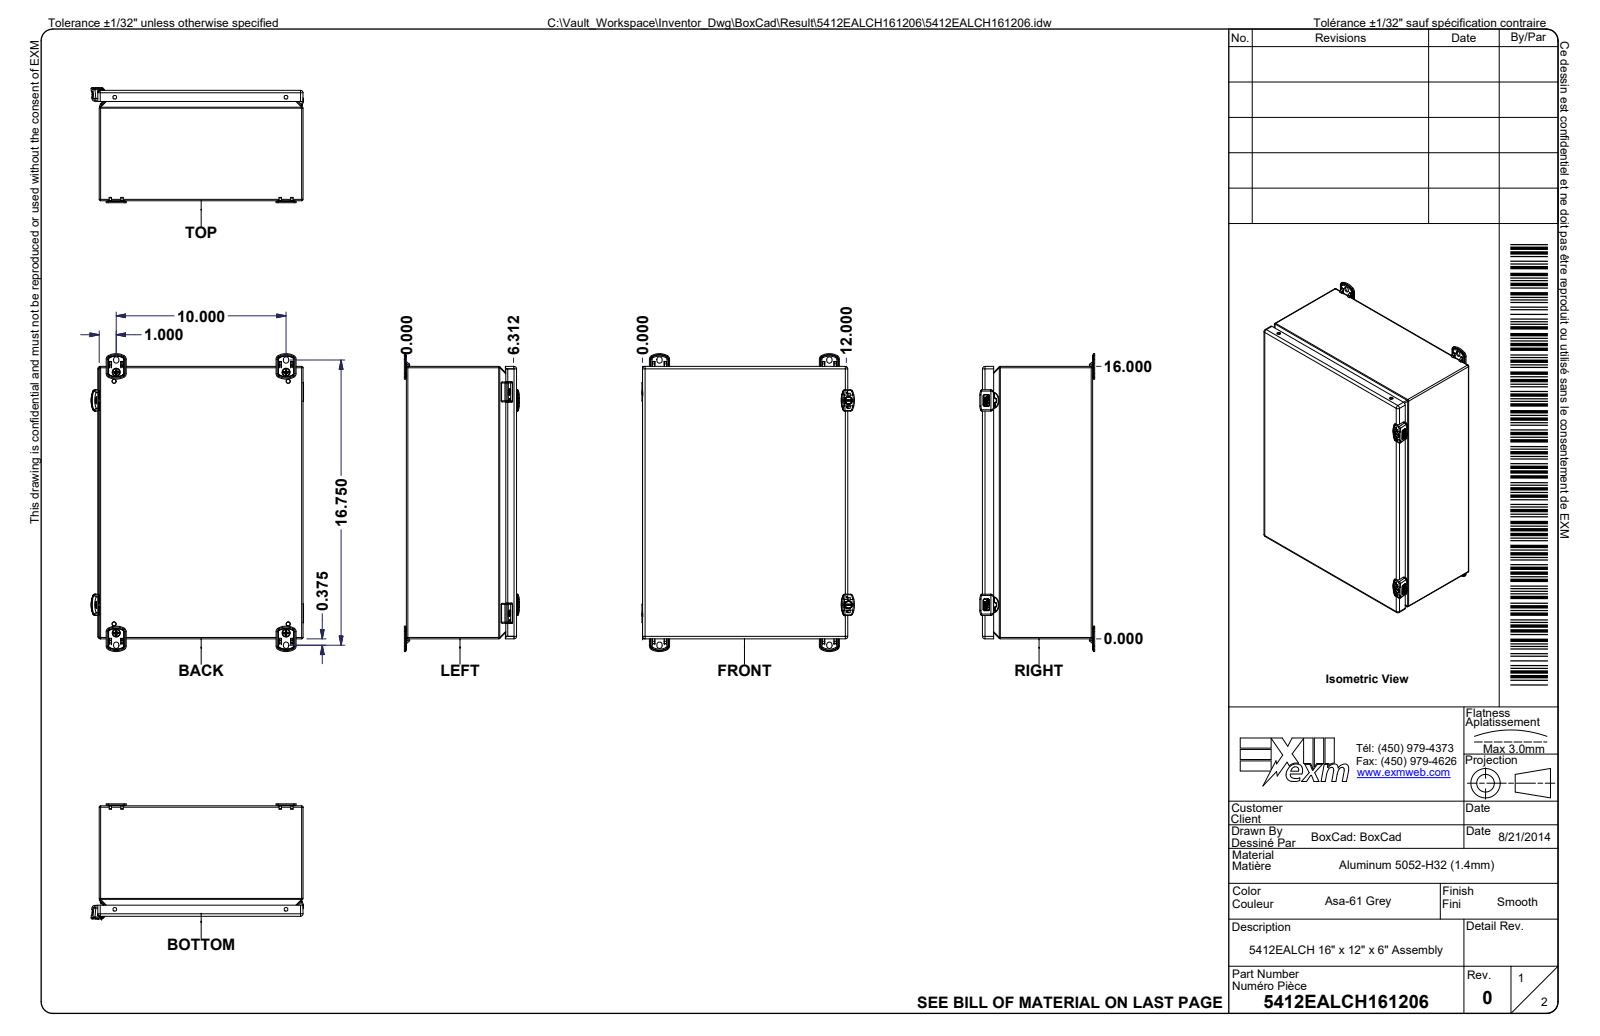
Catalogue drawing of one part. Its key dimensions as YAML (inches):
part_name: "5412EALCH161206; 5412EALCH161206B; 5412EALCH161206B-P; STK-A-70469-1 (+8 more)"
step_written_by: "Autodesk Inventor 2020 (AUTOMOTIVE_DESIGN)"
units: inches
bodies: {solids: 59, faces: 8409, planar: 3583, cylindrical: 2002, other: 2824}
overall_size: [17.496, 12.503, 6.76]
volume: 57.28
surface_area: 2034
round_holes:
  - {diameter: 0.165, count: 4}
  - {diameter: 0.173, count: 4}
  - {diameter: 0.197, count: 4}
  - {diameter: 0.197, count: 4}
  - {diameter: 0.236, count: 4}
  - {diameter: 0.236, count: 4}
  - {diameter: 0.32, count: 4}
  - {diameter: 0.03, count: 2}
  - {diameter: 0.175, count: 2}
  - {diameter: 0.201, count: 2}
  - {diameter: 0.24, count: 2}
  - {diameter: 0.339, count: 2}
round_bosses_or_shafts:
  - {diameter: 0.232, count: 8}
  - {diameter: 0.5, count: 4}
  - {diameter: 0.3, count: 4}
  - {diameter: 0.236, count: 4}
  - {diameter: 0.193, count: 4}
  - {diameter: 0.197, count: 3}
  - {diameter: 0.412, count: 2}
  - {diameter: 0.394, count: 2}
partial_cylinders:
  - {radius: 0.02, count: 257}
  - {radius: 0.01, count: 209}
  - {radius: 0.039, count: 92}
  - {radius: 0.004, count: 64}
  - {radius: 0.008, count: 60}
  - {radius: 0.059, count: 57}
  - {radius: 0.031, count: 35}
  - {radius: 0.005, count: 33}
face_to_face_distances: [0.053, 0.053, 6.433, 6.38, 6.486, 6.433, 11.947, 0.236, 0.304, 0.357]
hole_center_spacings: [0.546, 10.139, 14.781, 17.916, 1.507, 10.25, 10.25, 13.163]
